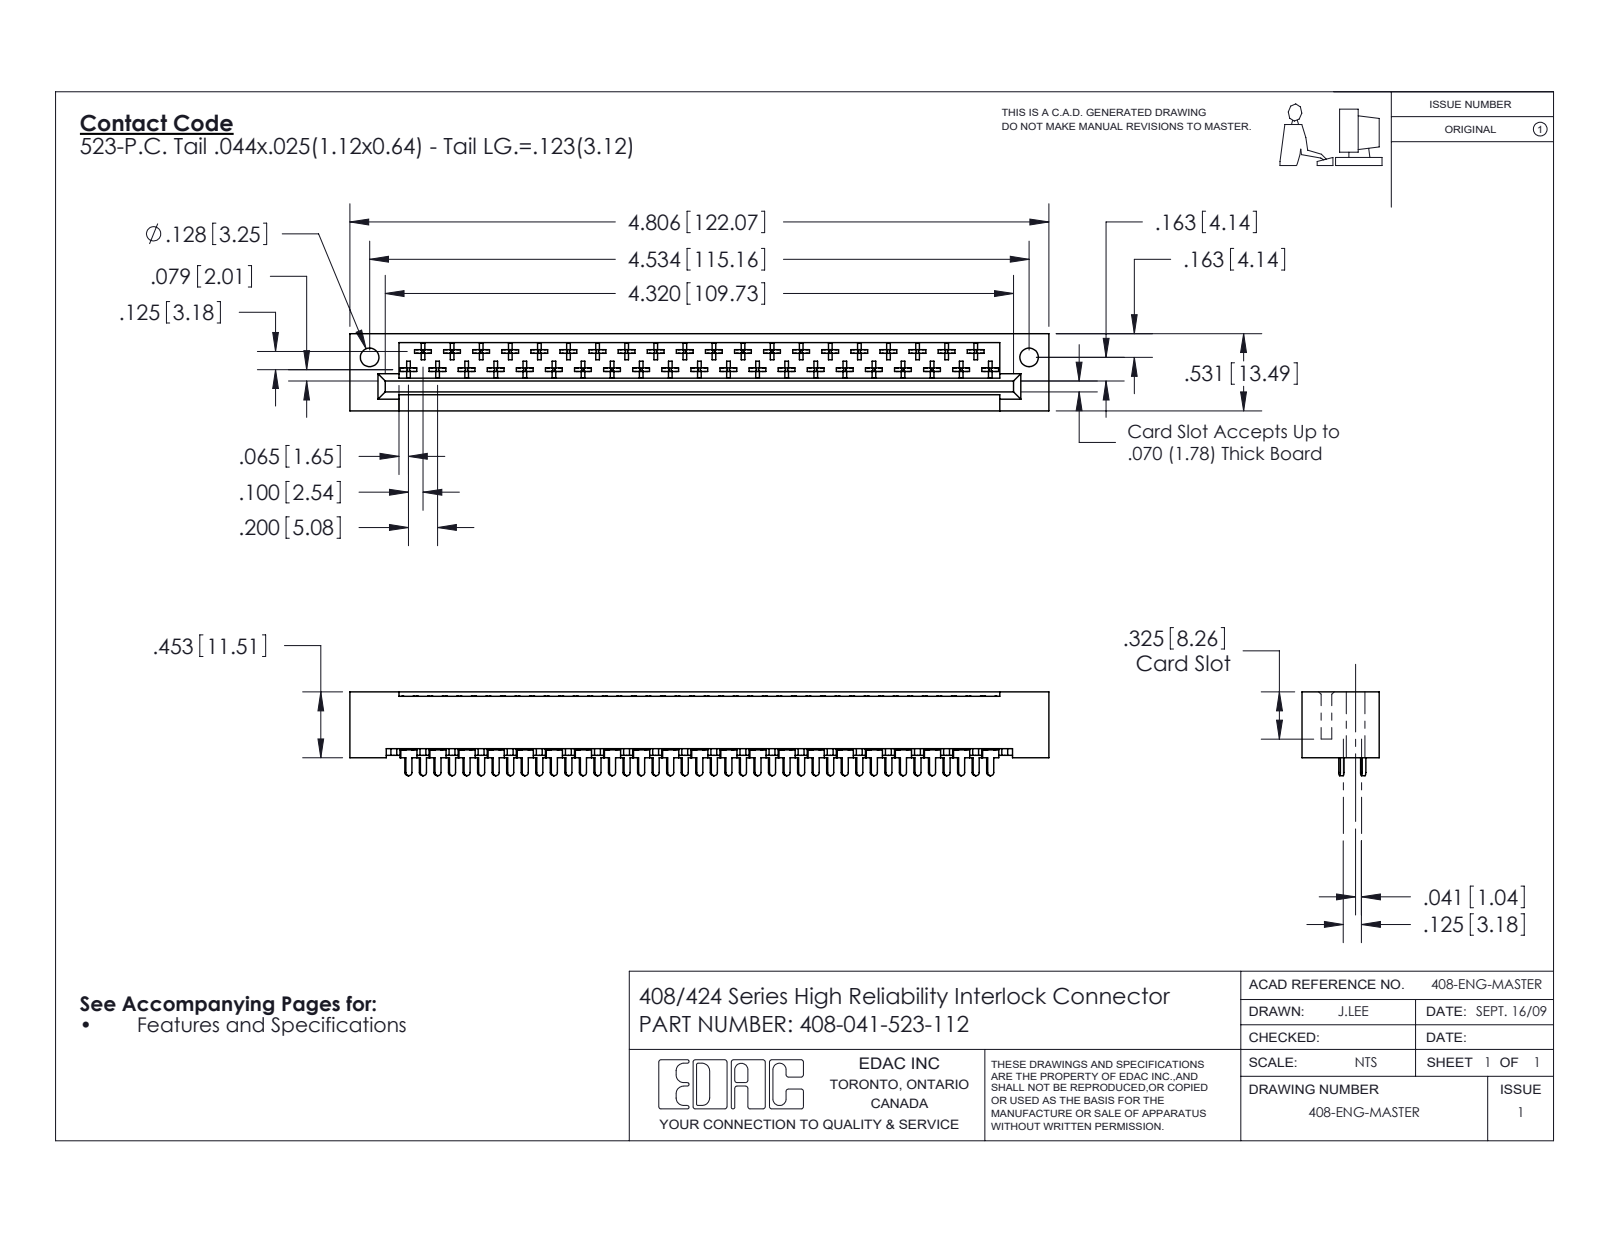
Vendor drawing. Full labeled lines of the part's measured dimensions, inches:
Part name (STEP PRODUCT): 408-290-001_408-290-123 - Top; 408 Part_041 - 1; 408-290-001_408-290-123 - Bottom; 408-047-523-112
STEP written by: SolidWorks 2016 (CONFIG_CONTROL_DESIGN)
Units: inches
Bodies: 42 solids, 2299 faces (1758 planar, 377 cylindrical, 164 other)
Overall size (bounding box): 4.806 × 0.576 × 0.531
Volume: 0.849 in³ · Surface area: 25.75 in²
Round holes (diameter × count): ⌀0.128 ×2
Partial cylindrical surfaces — rounded edges, fillets, slot ends (radius × count): R0.01 ×246, R0.02 ×43, R0.022 ×41
Main face-to-face distances: 0.531, 0.125, 0.1, 0.025, 0.025, 0.4, 0.259, 0.272, 0.235, 0.296
Hole centre spacings: 4.534
